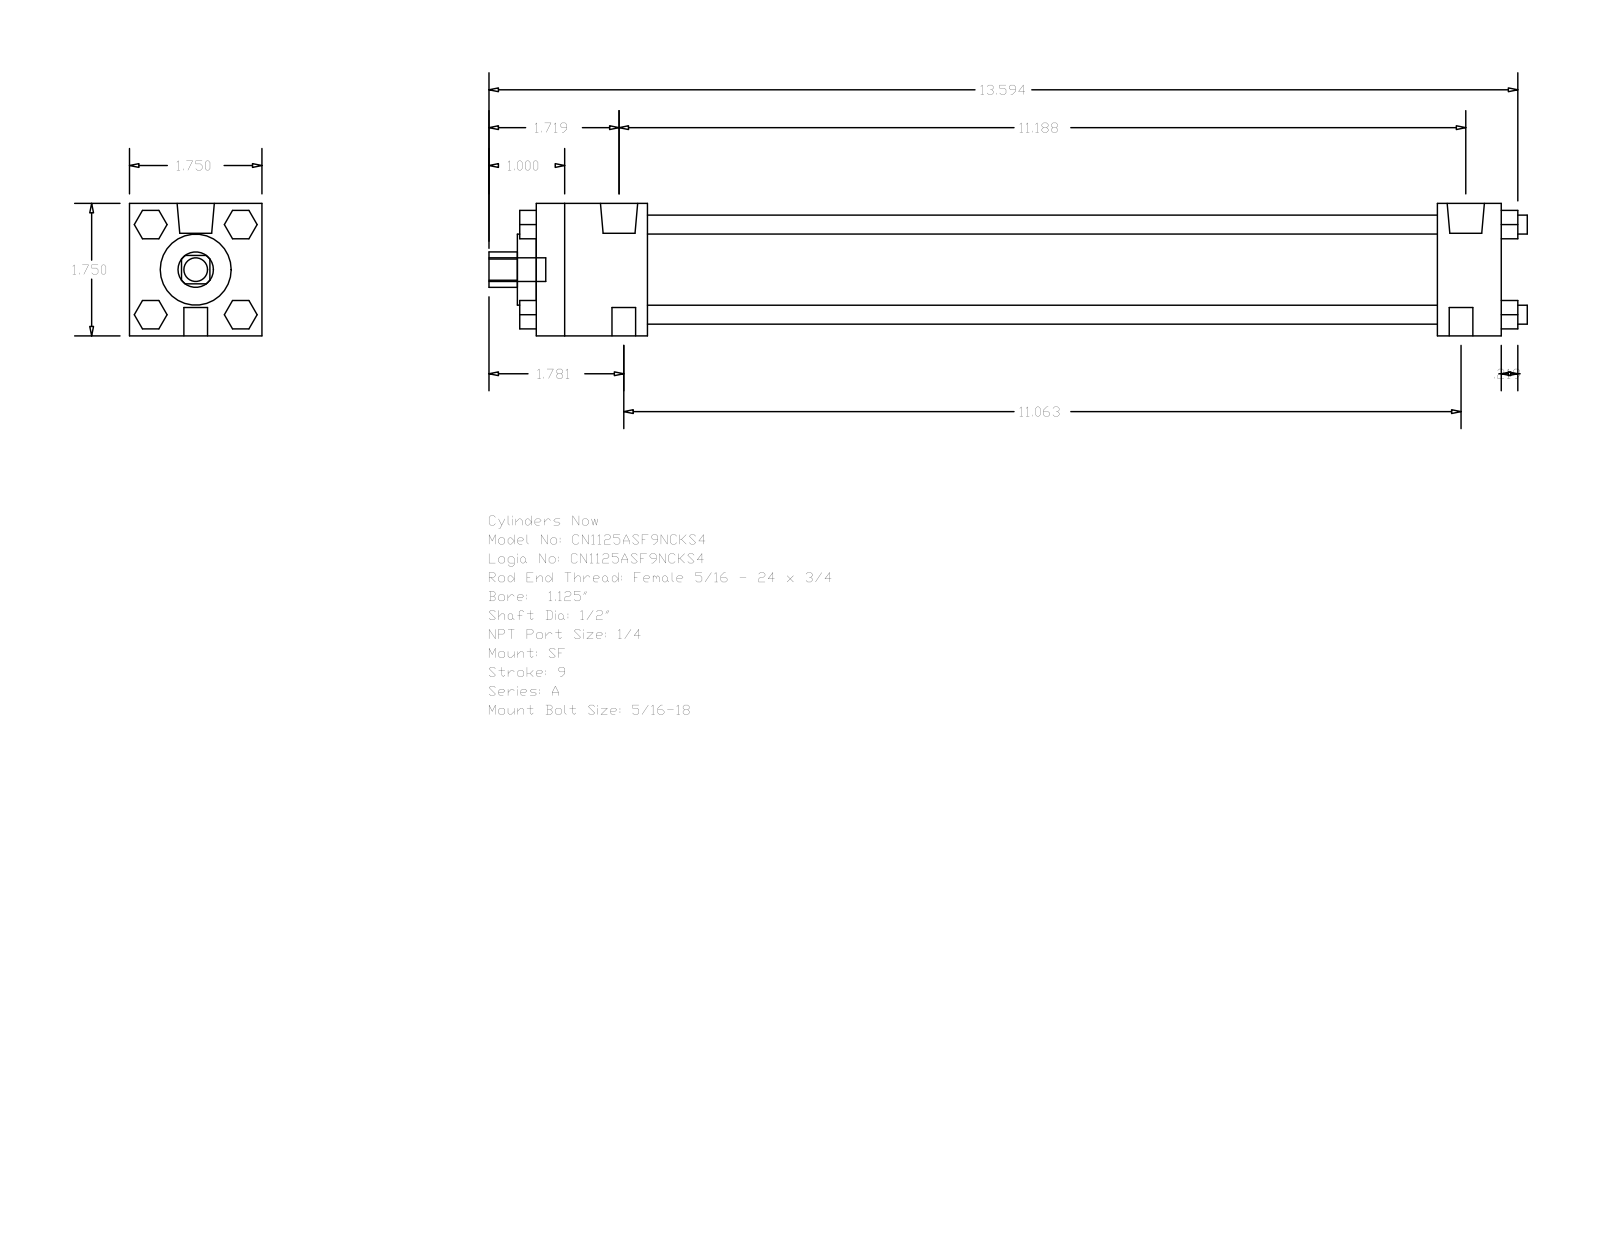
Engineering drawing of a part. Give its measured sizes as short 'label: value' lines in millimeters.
name: A_SF__0112_0.5
written by: GSSL Pune (CONFIG_CONTROL_DESIGN)
unit: mm
bodies: 0 solids, 120 faces (92 planar, 28 cylindrical, 0 other)
size: 348.46 × 44.45 × 44.45
holes: 1× ⌀12.7, 1× ⌀23.81, 1× ⌀31.88
bosses: 4× ⌀6.35, 3× ⌀7.94, 2× ⌀12.49, 2× ⌀5.56
rounds: 1× R5.94
face distances: 44.46, 323.85, 302.41, 21.44, 37.3, 265.11, 286.55, 9.53, 5.59, 9.52
